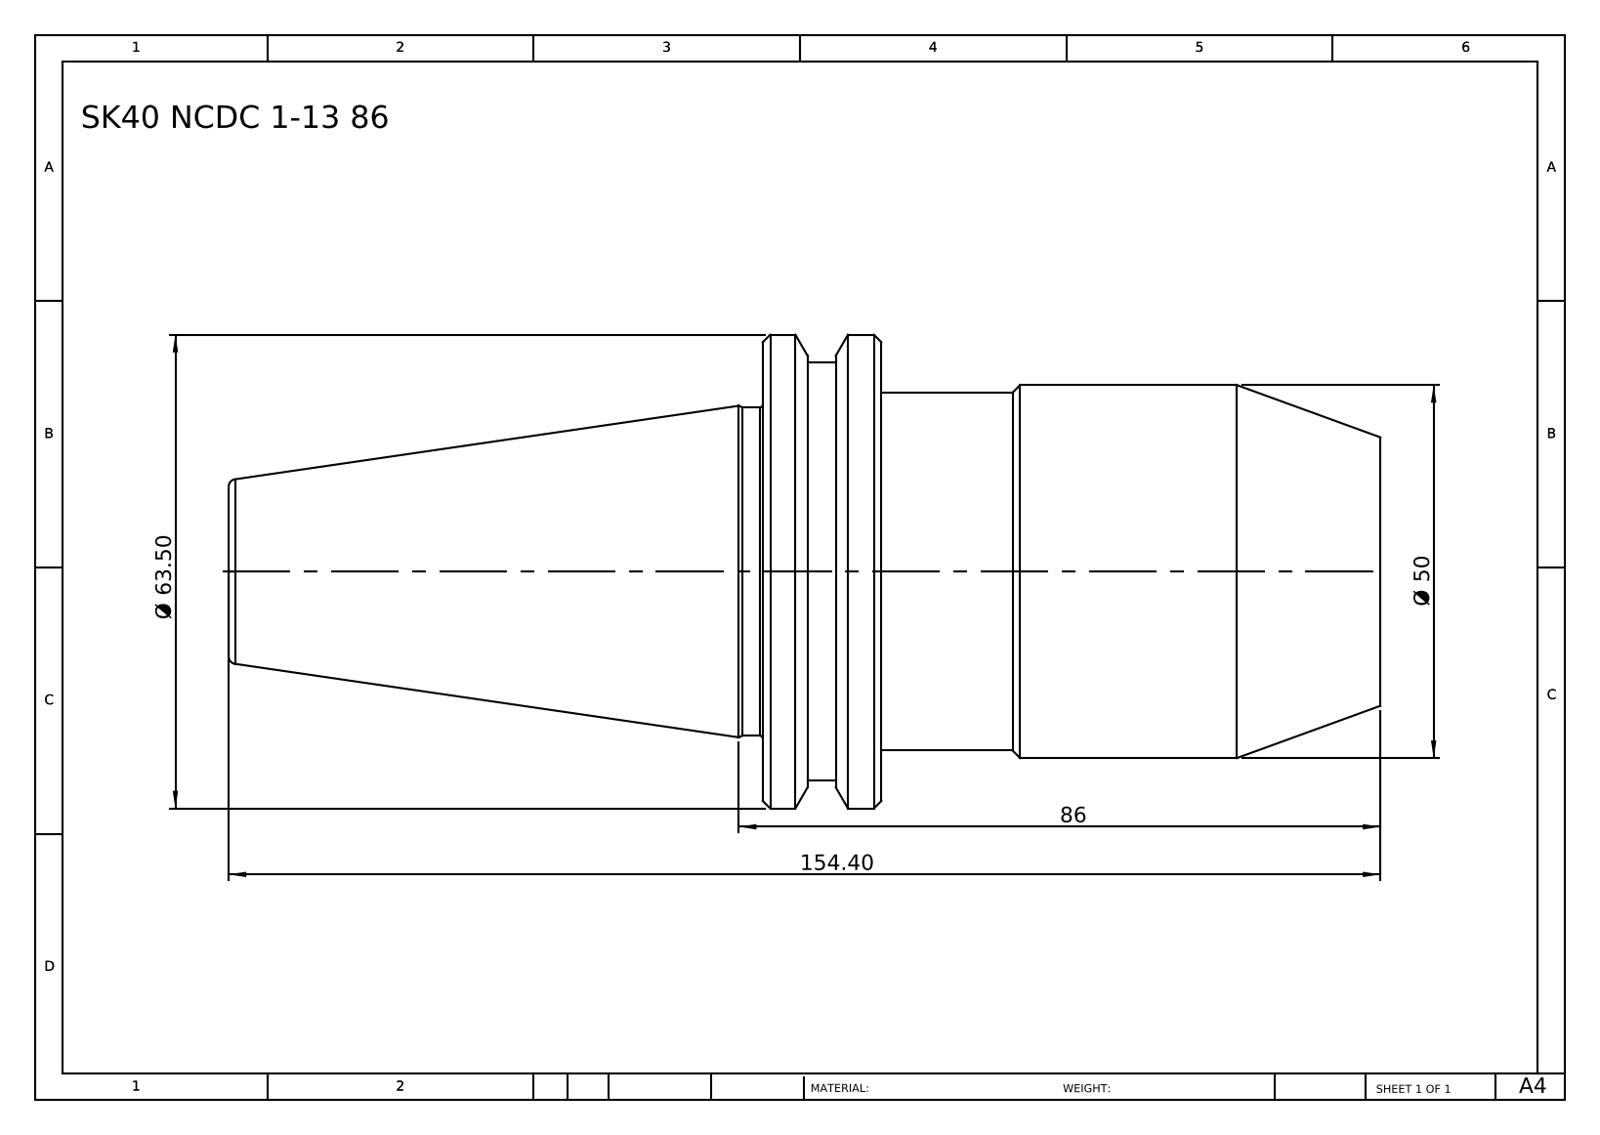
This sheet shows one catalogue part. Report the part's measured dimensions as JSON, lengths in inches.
{"part_name": "SK40 NCDC1-13 86", "step_written_by": "SolidWorks 2014 (CONFIG_CONTROL_DESIGN)", "units": "inches", "bodies": {"solids": 1, "faces": 38, "planar": 6, "cylindrical": 12, "other": 20}, "overall_size": [6.079, 2.5, 2.5], "volume_in3": 14.41, "surface_area_in2": 40.85, "round_bosses_or_shafts": [[2.5, 1], [2.205, 1], [1.969, 1], [1.89, 1], [1.732, 1]], "face_to_face_distances": [0.626, 2.634, 3.26, 6.079, 3.445, 2.819, 3.024, 0.39, 0.236, 3.055]}
